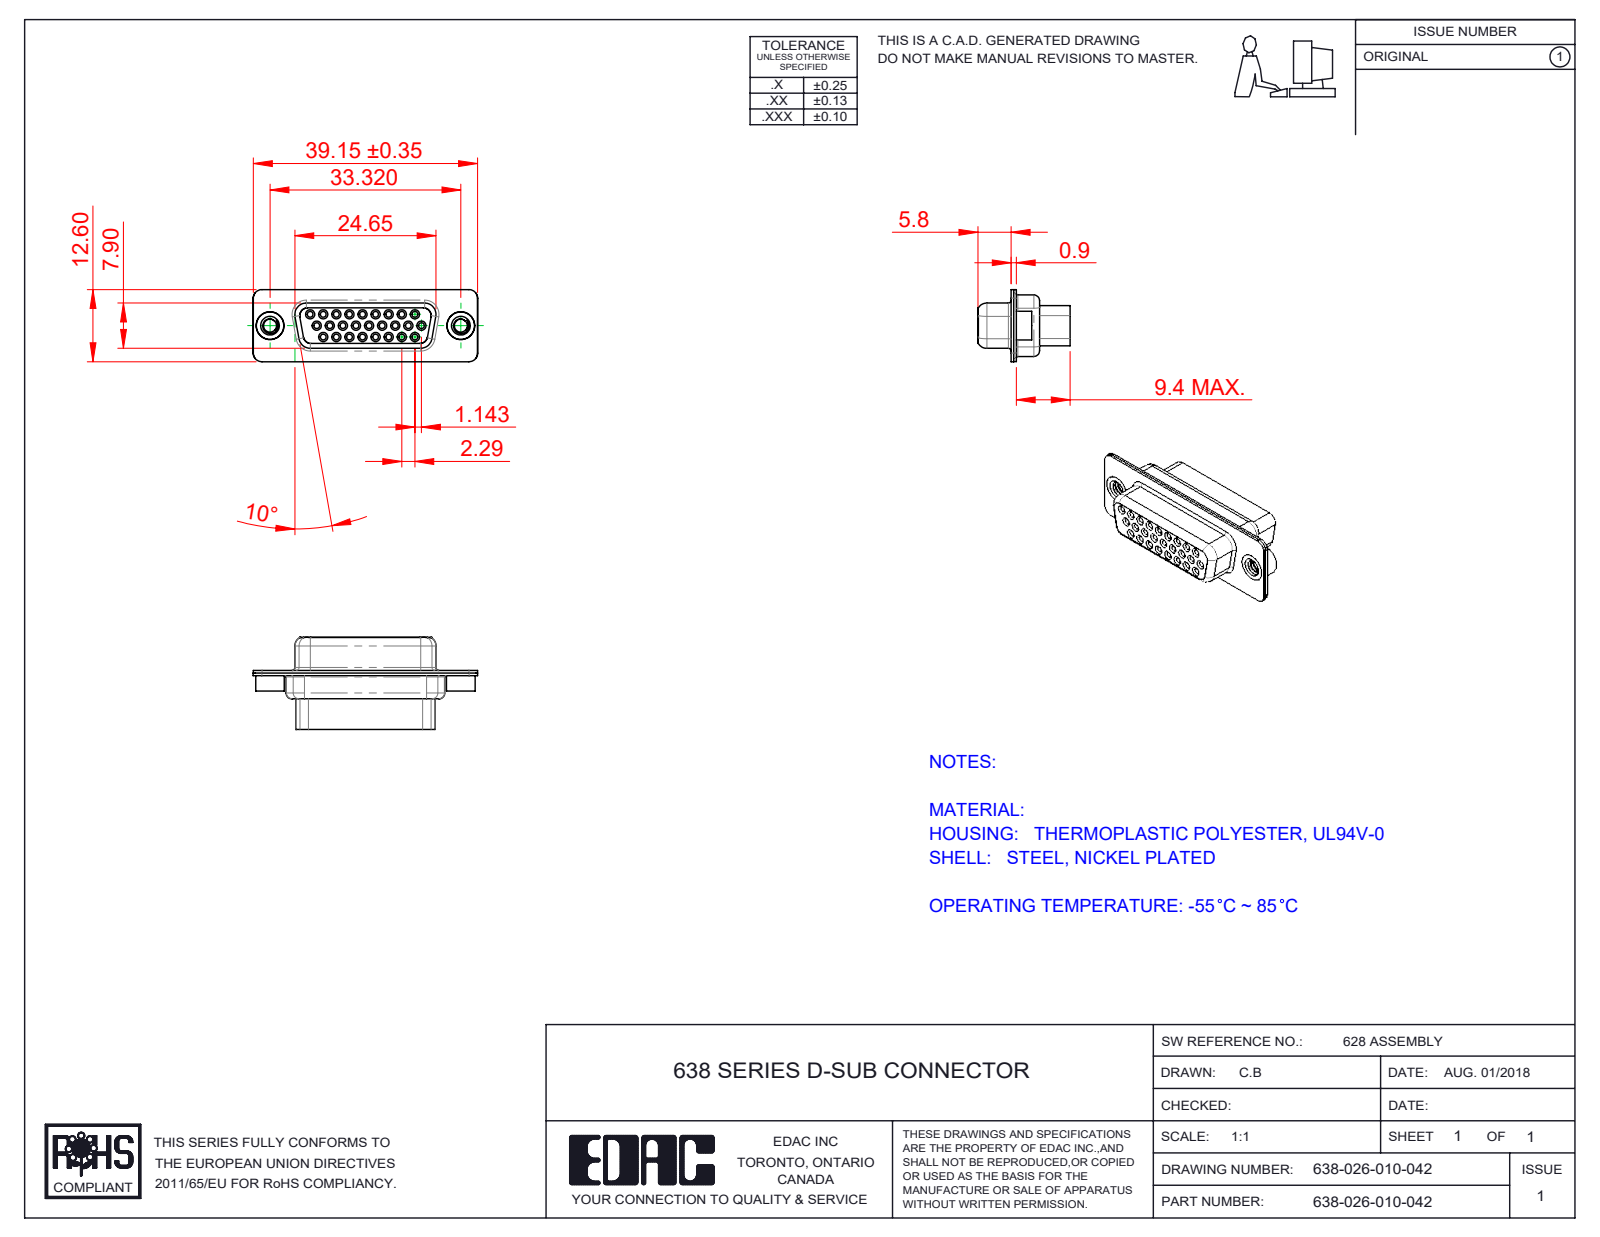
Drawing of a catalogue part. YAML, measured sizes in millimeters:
part_name: "638 Shell Rear_26 Contacts; 638 Housing_26 Contacts HP; 638 Shell Front_26 Contacts; 638-026-010-042 (+1 more)"
step_written_by: "SolidWorks 2020 (CONFIG_CONTROL_DESIGN)"
units: millimeters
bodies: {solids: 5, faces: 617, planar: 145, cylindrical: 345, other: 127}
overall_size: [39.19, 16.1, 12.6]
volume: 2379
surface_area: 6439
round_holes:
  - {diameter: 1, count: 26}
  - {diameter: 1.7, count: 26}
  - {diameter: 1.8, count: 26}
  - {diameter: 2, count: 26}
  - {diameter: 2.26, count: 2}
  - {diameter: 4, count: 2}
  - {diameter: 4.05, count: 2}
  - {diameter: 4.85, count: 2}
round_bosses_or_shafts:
  - {diameter: 5, count: 2}
  - {diameter: 4.95, count: 2}
  - {diameter: 4.8, count: 2}
partial_cylinders:
  - {radius: 1.5, count: 20}
  - {radius: 2, count: 12}
  - {radius: 1.55, count: 8}
  - {radius: 1.35, count: 5}
  - {radius: 0.25, count: 4}
  - {radius: 0.5, count: 4}
  - {radius: 0.55, count: 4}
  - {radius: 0.7, count: 4}
face_to_face_distances: [0.45, 0.4, 6.6, 0.9, 1.43, 8.88, 7, 9.4, 6.2, 0.85]
hole_center_spacings: [3.96, 2.28, 4.57, 6.05, 2.29, 8.24, 6.86, 10.48]
